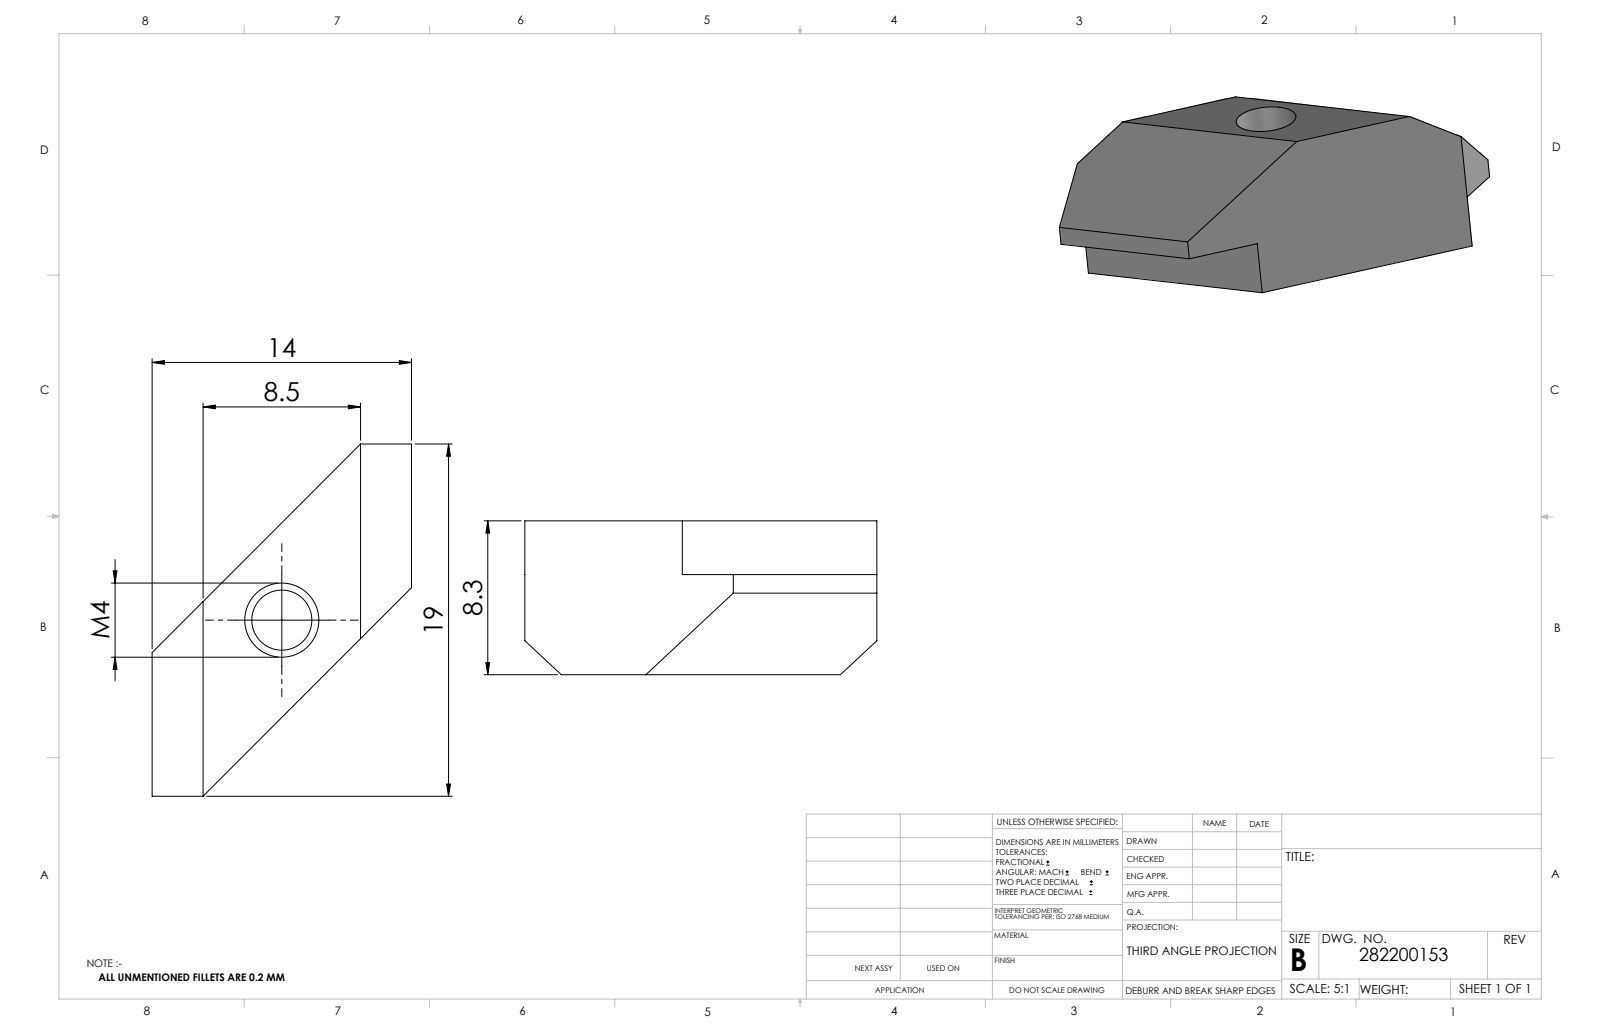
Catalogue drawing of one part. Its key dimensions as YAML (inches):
part_name: "282200153_c_1"
step_written_by: "SolidWorks 2014 (AUTOMOTIVE_DESIGN)"
units: inches
bodies: {solids: 1, faces: 18, planar: 14, cylindrical: 2, other: 2}
overall_size: [0.748, 0.551, 0.327]
volume: 0.046
surface_area: 1.04
round_holes:
  - {diameter: 0.128, count: 1}
face_to_face_distances: [0.292, 0.114, 0.213, 0.327, 0.335, 0.108, 0.443, 0.551, 0.748]
